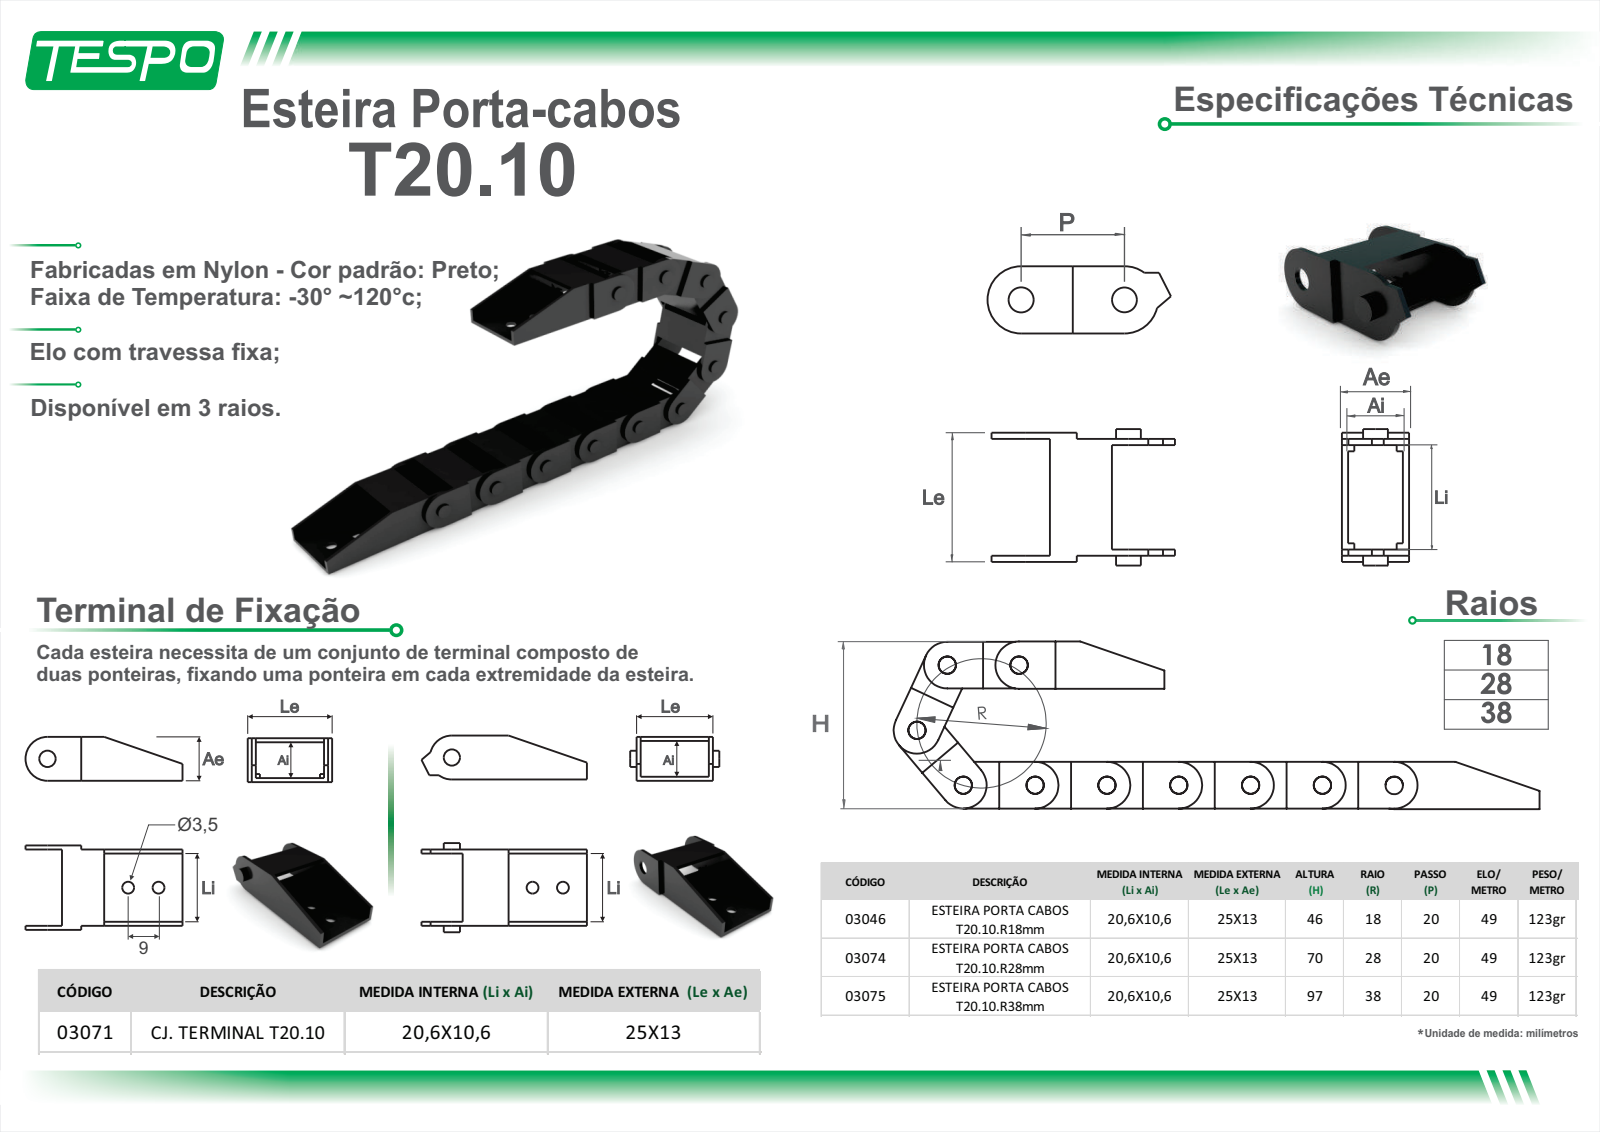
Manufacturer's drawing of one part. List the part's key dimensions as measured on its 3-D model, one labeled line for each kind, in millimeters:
STEP written by: ST-DEVELOPER v15 (AUTOMOTIVE_DESIGN)
Units: millimetres
Bodies: 1 solid, 34 faces (22 planar, 0 cylindrical, 12 other)
Overall size (bounding box): 33 × 26.4 × 13
Volume: 1 609 mm³ · Surface area: 2 900 mm²
Main face-to-face distances: 1.2, 22.6, 11.8, 21.4, 2.4, 23.8, 13, 10.6, 20.2, 25
